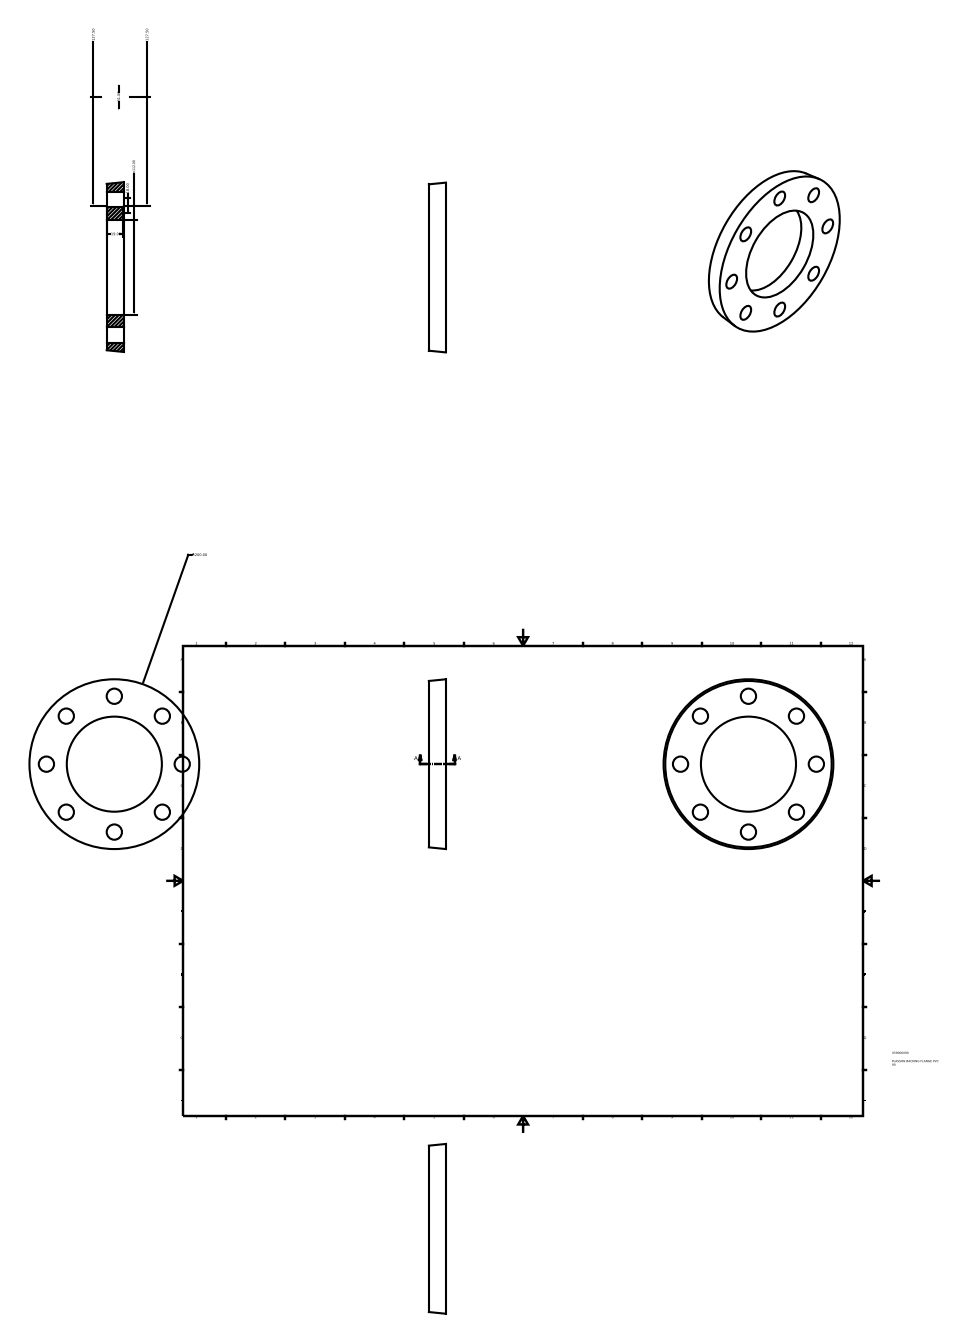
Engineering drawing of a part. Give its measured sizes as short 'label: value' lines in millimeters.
name: 059000090
written by: Autodesk Inventor 2015 (AUTOMOTIVE_DESIGN)
unit: mm
bodies: 1 solid, 12 faces (2 planar, 9 cylindrical, 1 other)
size: 200 × 200 × 20
volume: 378 080 mm³; area: 66 400 mm²
holes: 8× ⌀18, 1× ⌀112
face distances: 20
hole spacings: 61.23, 80, 113.14, 147.82, 160
